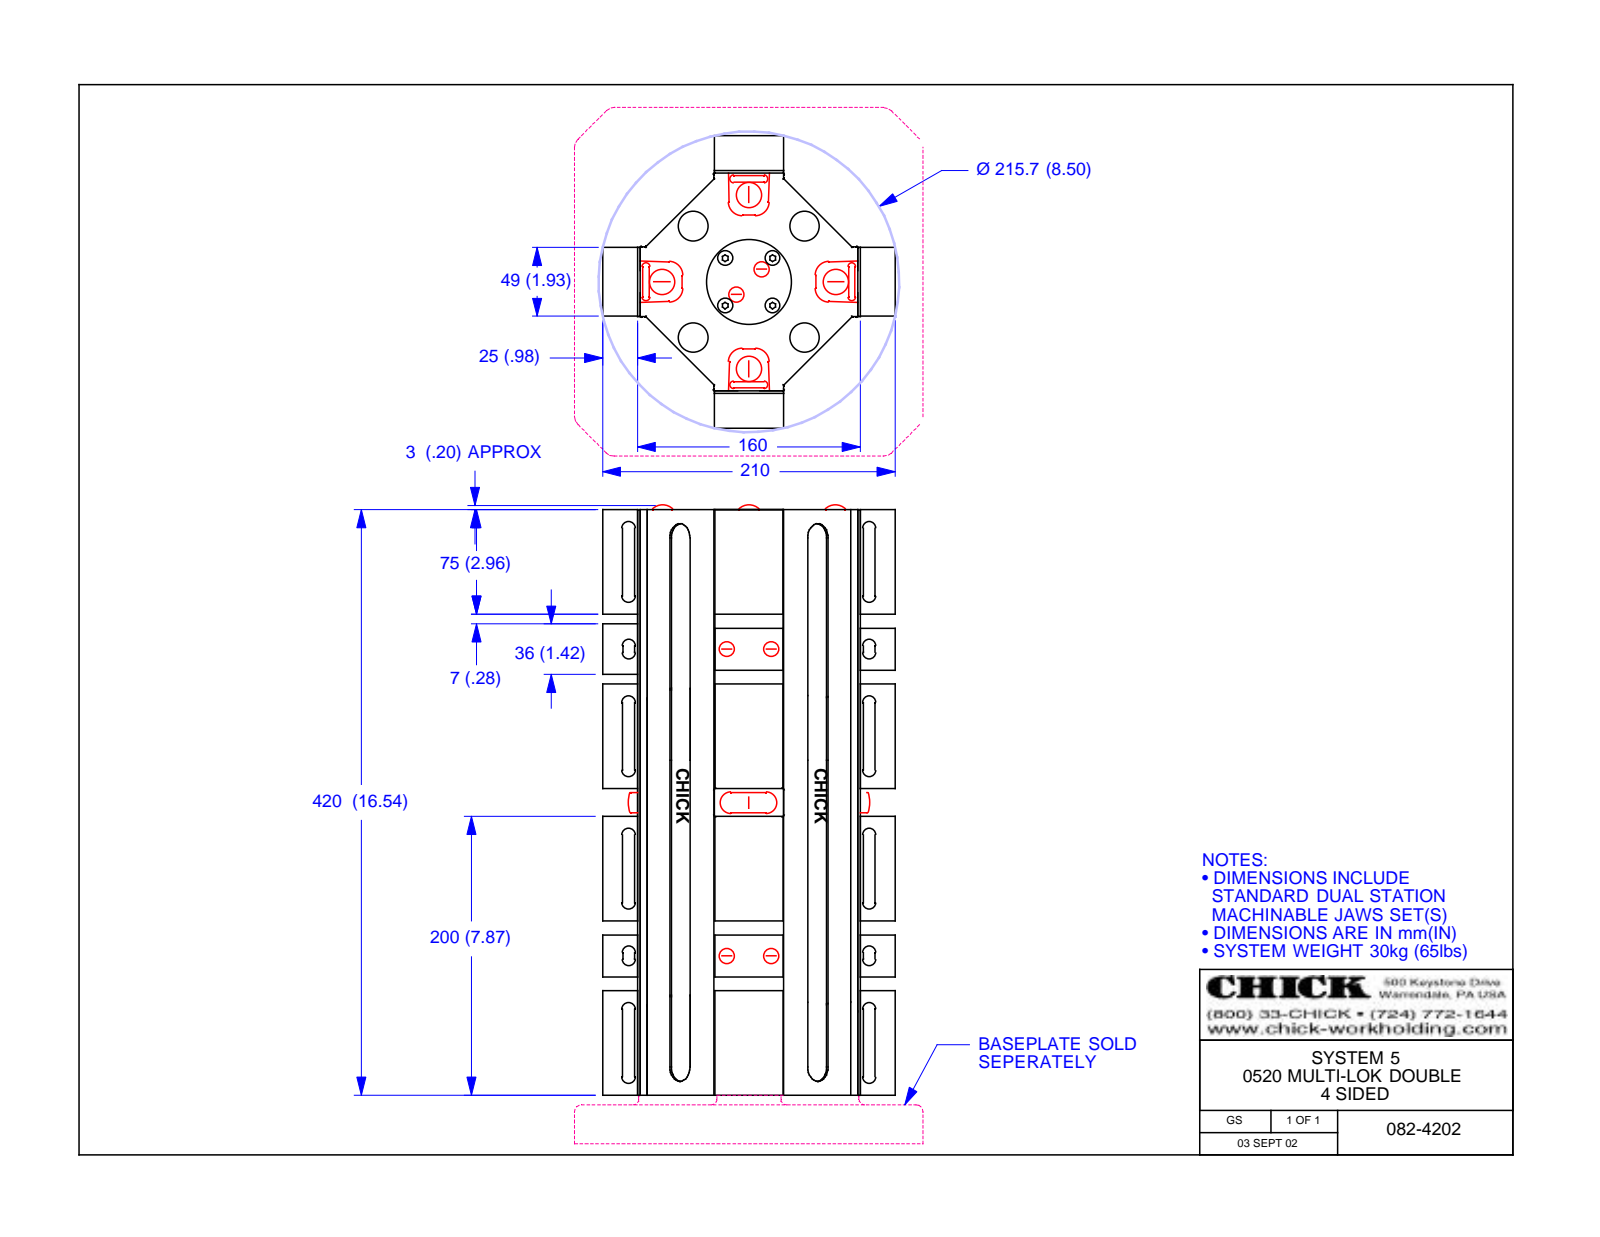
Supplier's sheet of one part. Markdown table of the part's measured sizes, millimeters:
| quantity | value |
| --- | --- |
| part name | 082-4202; 082-4212; 080-0313-21; 080-2500 (+2 more) |
| STEP written by | Autodesk Inventor 2013 (AUTOMOTIVE_DESIGN) |
| units | millimeters |
| bodies | 33 solids, 3556 faces (1328 planar, 863 cylindrical, 1365 other) |
| overall size | 424 × 210 × 210 |
| volume | 8 192 000 mm³ |
| surface area | 926 265 mm² |
| round holes (diameter × count) | 4.13 × 24, 10 × 24, 12.7 × 24, 5.2 × 8, 9.14 × 8, 9.65 × 8, 10.11 × 8, 20 × 8, 13.5 × 5, 8.12 × 4, 13.74 × 4, 18.09 × 4 |
| round bosses / shafts (diameter × count) | 14 × 24, 15.34 × 4, 9.52 × 4 |
| partial cylindrical surfaces (radius × count) | 0.8 × 208, 1 × 40, 1.9 × 16, 2.4 × 16, 5 × 16, 3.29 × 8, 5.67 × 8, 7.9 × 8 |
| main face-to-face distances | 2, 158, 72.99, 87.01, 70.99, 85.01, 183, 27, 25, 97.99 |
| hole center spacings | 75, 81.54, 32, 220, 222.32, 2.43, 18.03, 55.9 |
